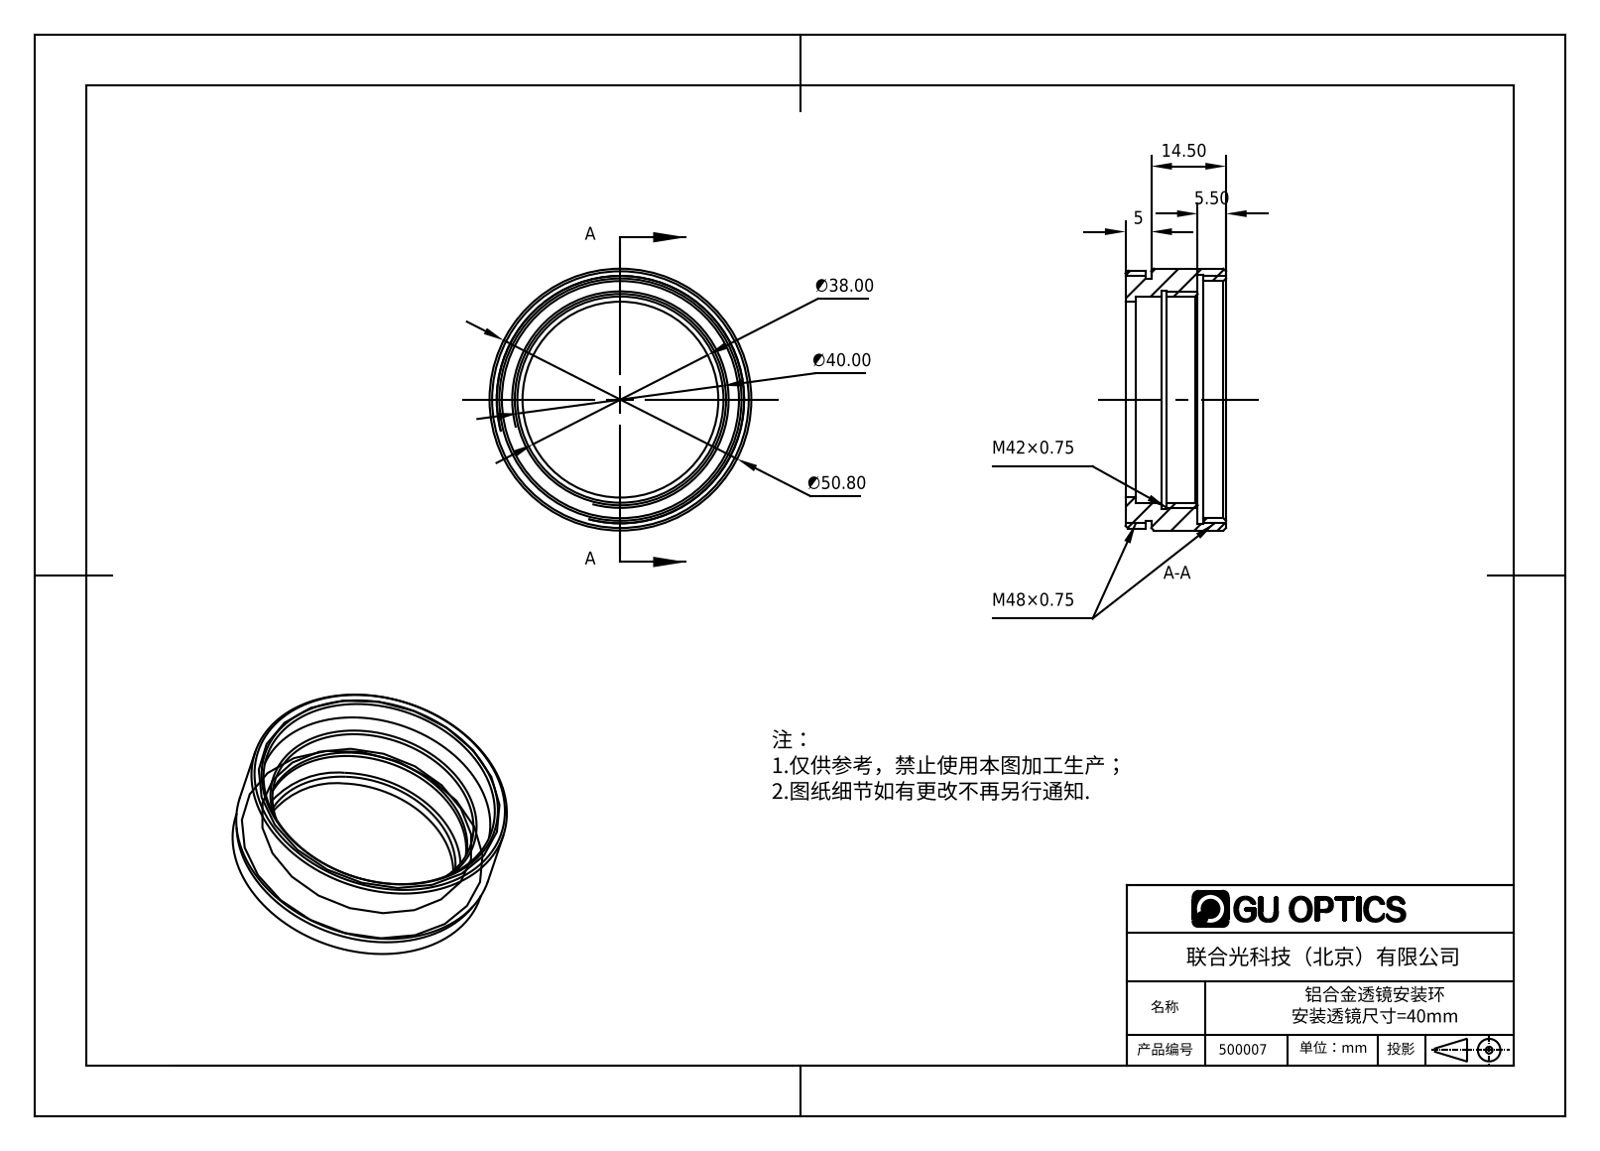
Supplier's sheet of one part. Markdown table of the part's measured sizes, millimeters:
| quantity | value |
| --- | --- |
| part name | 500007 |
| STEP written by | SolidWorks 2016 (AUTOMOTIVE_DESIGN) |
| units | millimeters |
| bodies | 1 solid, 37 faces (9 planar, 18 cylindrical, 10 other) |
| overall size | 50.8 × 50.8 × 19.5 |
| volume | 12 077 mm³ |
| surface area | 8 308 mm² |
| round holes (diameter × count) | 38 × 1, 40 × 1, 42.3 × 1, 46 × 1, 48.3 × 1 |
| round bosses / shafts (diameter × count) | 50.8 × 1, 50 × 1, 47 × 1 |
| main face-to-face distances | 1, 14, 7, 3, 10, 2, 4, 5, 8, 6 |
